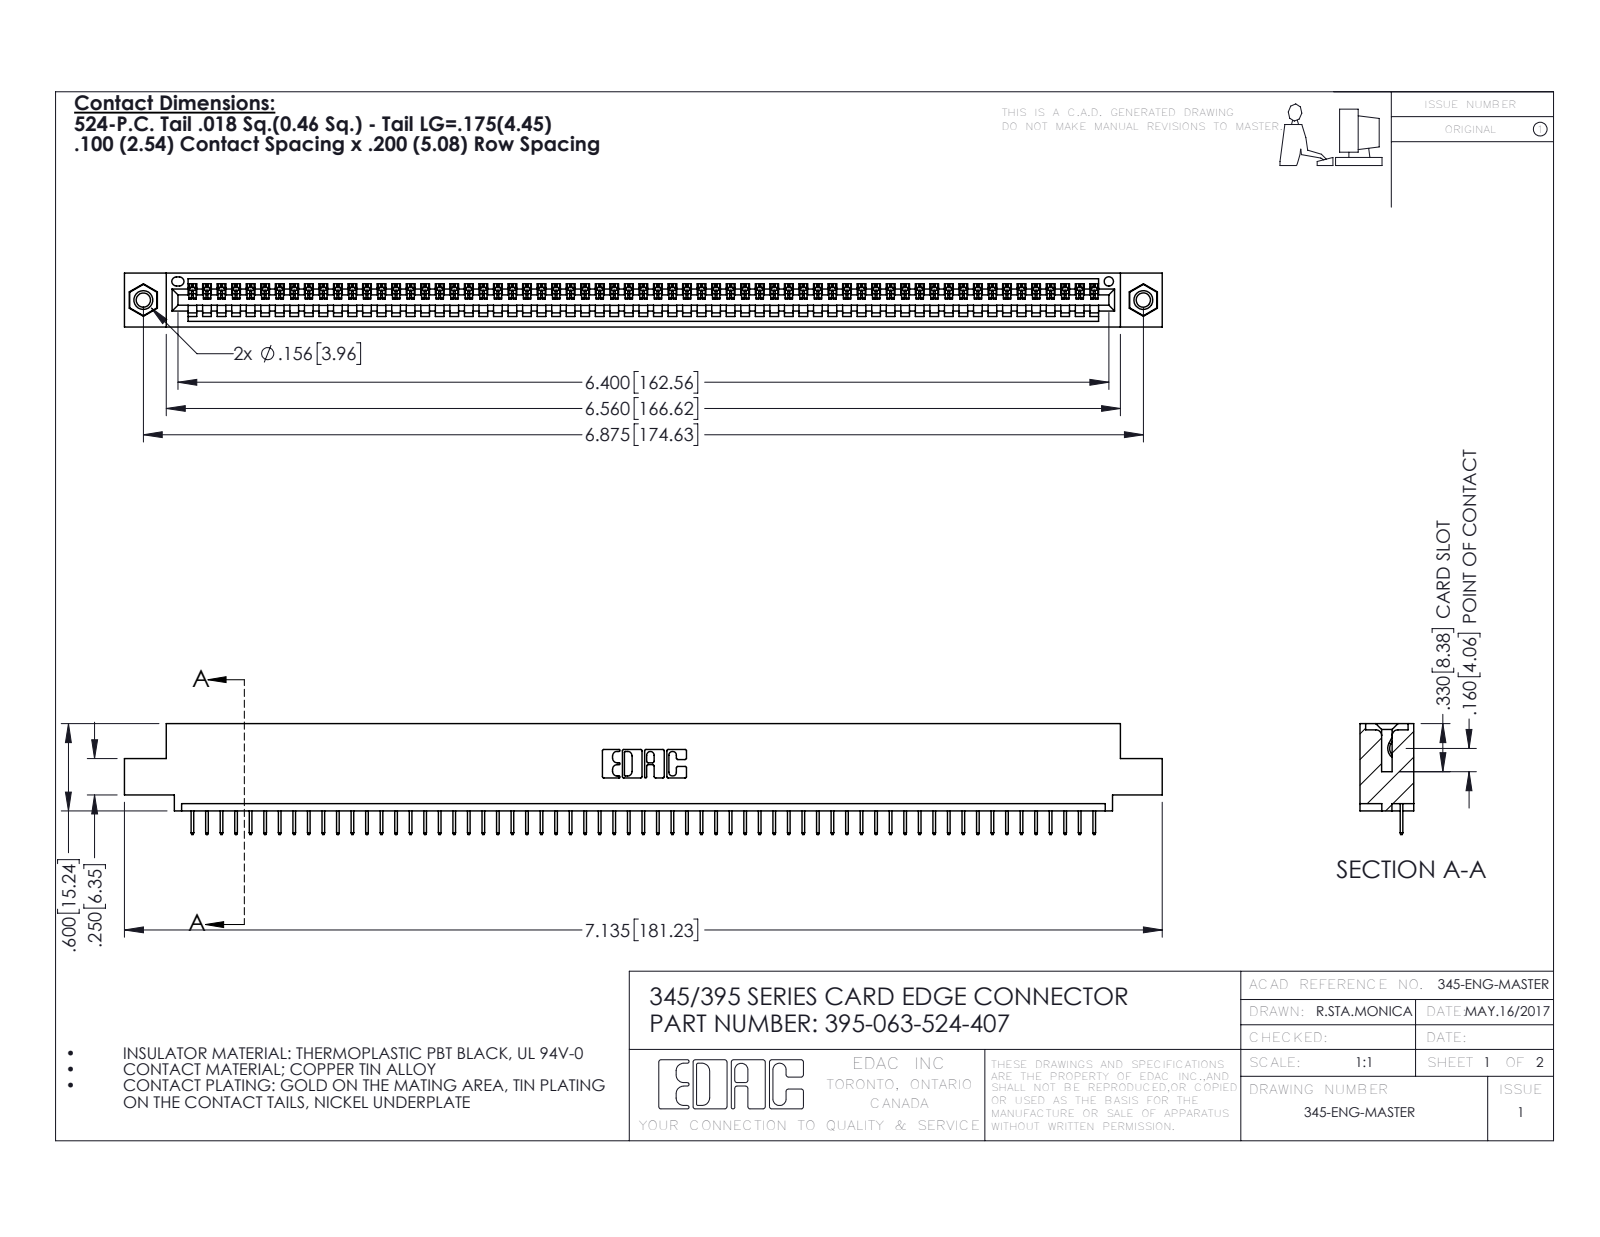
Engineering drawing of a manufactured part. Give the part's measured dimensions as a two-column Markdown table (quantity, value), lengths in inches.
| quantity | value |
| --- | --- |
| part name | 345 Part_0.110 Offset - 0.156 Dia-TI; 345-292-001_345-293-124; 345-250-001_345-250-005-103; 395-063-524-407 |
| STEP written by | SolidWorks 2016 (CONFIG_CONTROL_DESIGN) |
| units | inches |
| bodies | 66 solids, 4096 faces (3014 planar, 1066 cylindrical, 16 other) |
| overall size | 7.135 × 0.762 × 0.37 |
| volume | 1.04 in³ |
| surface area | 34.51 in² |
| round holes (diameter × count) | 0.098 × 2, 0.125 × 2, 0.156 × 2, 0.064 × 1 |
| round bosses / shafts (diameter × count) | 0.155 × 2 |
| partial cylindrical surfaces (radius × count) | 0.006 × 126, 0.01 × 22, 0.007 × 6, 0.031 × 6, 0.026 × 3, 0.031 × 2, 0.04 × 2, 0.014 × 1 |
| main face-to-face distances | 0.072, 0.298, 0.37, 0.2, 0.098, 0.272, 0.025, 0.225, 0.072, 0.149 |
| hole center spacings | 0.27, 6.639, 6.875 |
